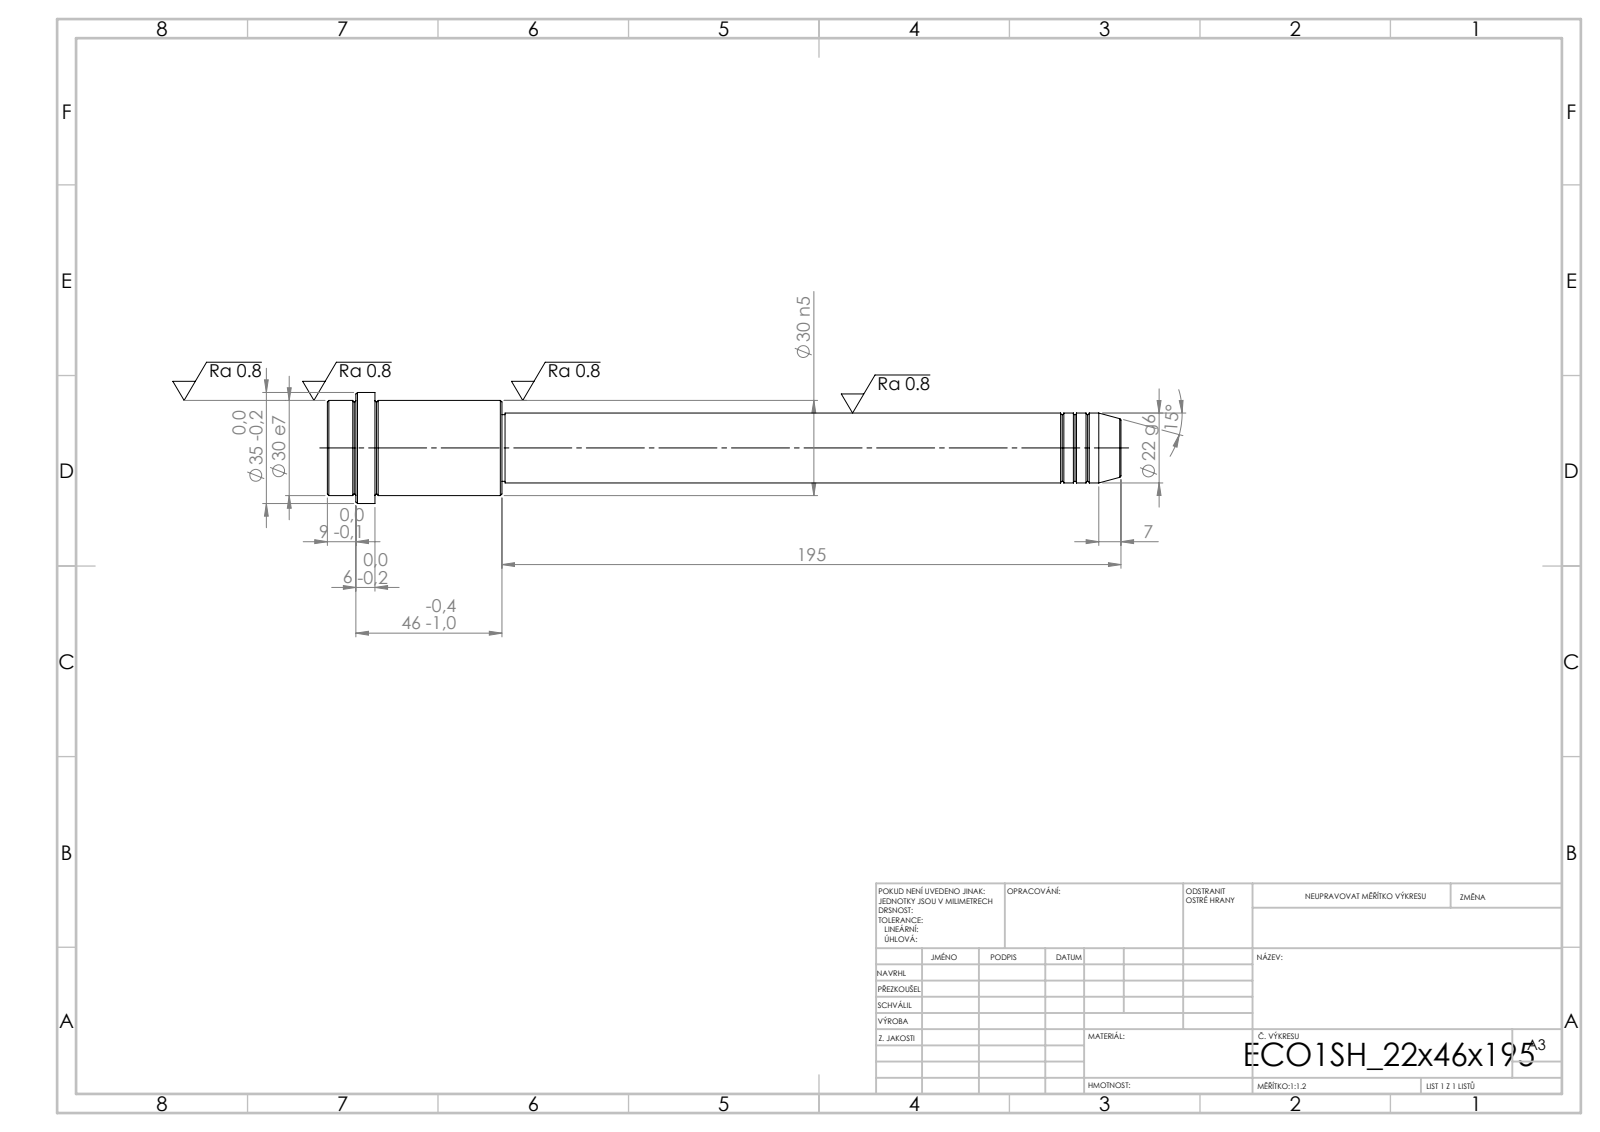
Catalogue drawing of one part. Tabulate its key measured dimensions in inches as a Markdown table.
| quantity | value |
| --- | --- |
| STEP written by | SolidWorks 2019 (CONFIG_CONTROL_DESIGN) |
| units | inches |
| bodies | 1 solid, 52 faces (6 planar, 16 cylindrical, 30 other) |
| overall size | 9.843 × 1.378 × 1.378 |
| volume | 6.95 in³ |
| surface area | 32.11 in² |
| round bosses / shafts (diameter × count) | 1.378 × 1, 1.181 × 1, 0.866 × 1, 0.827 × 1 |
| main face-to-face distances | 2.165, 1.575, 0.591, 7.677, 9.252, 9.843, 9.488, 1.811, 0.236, 0.354 |
